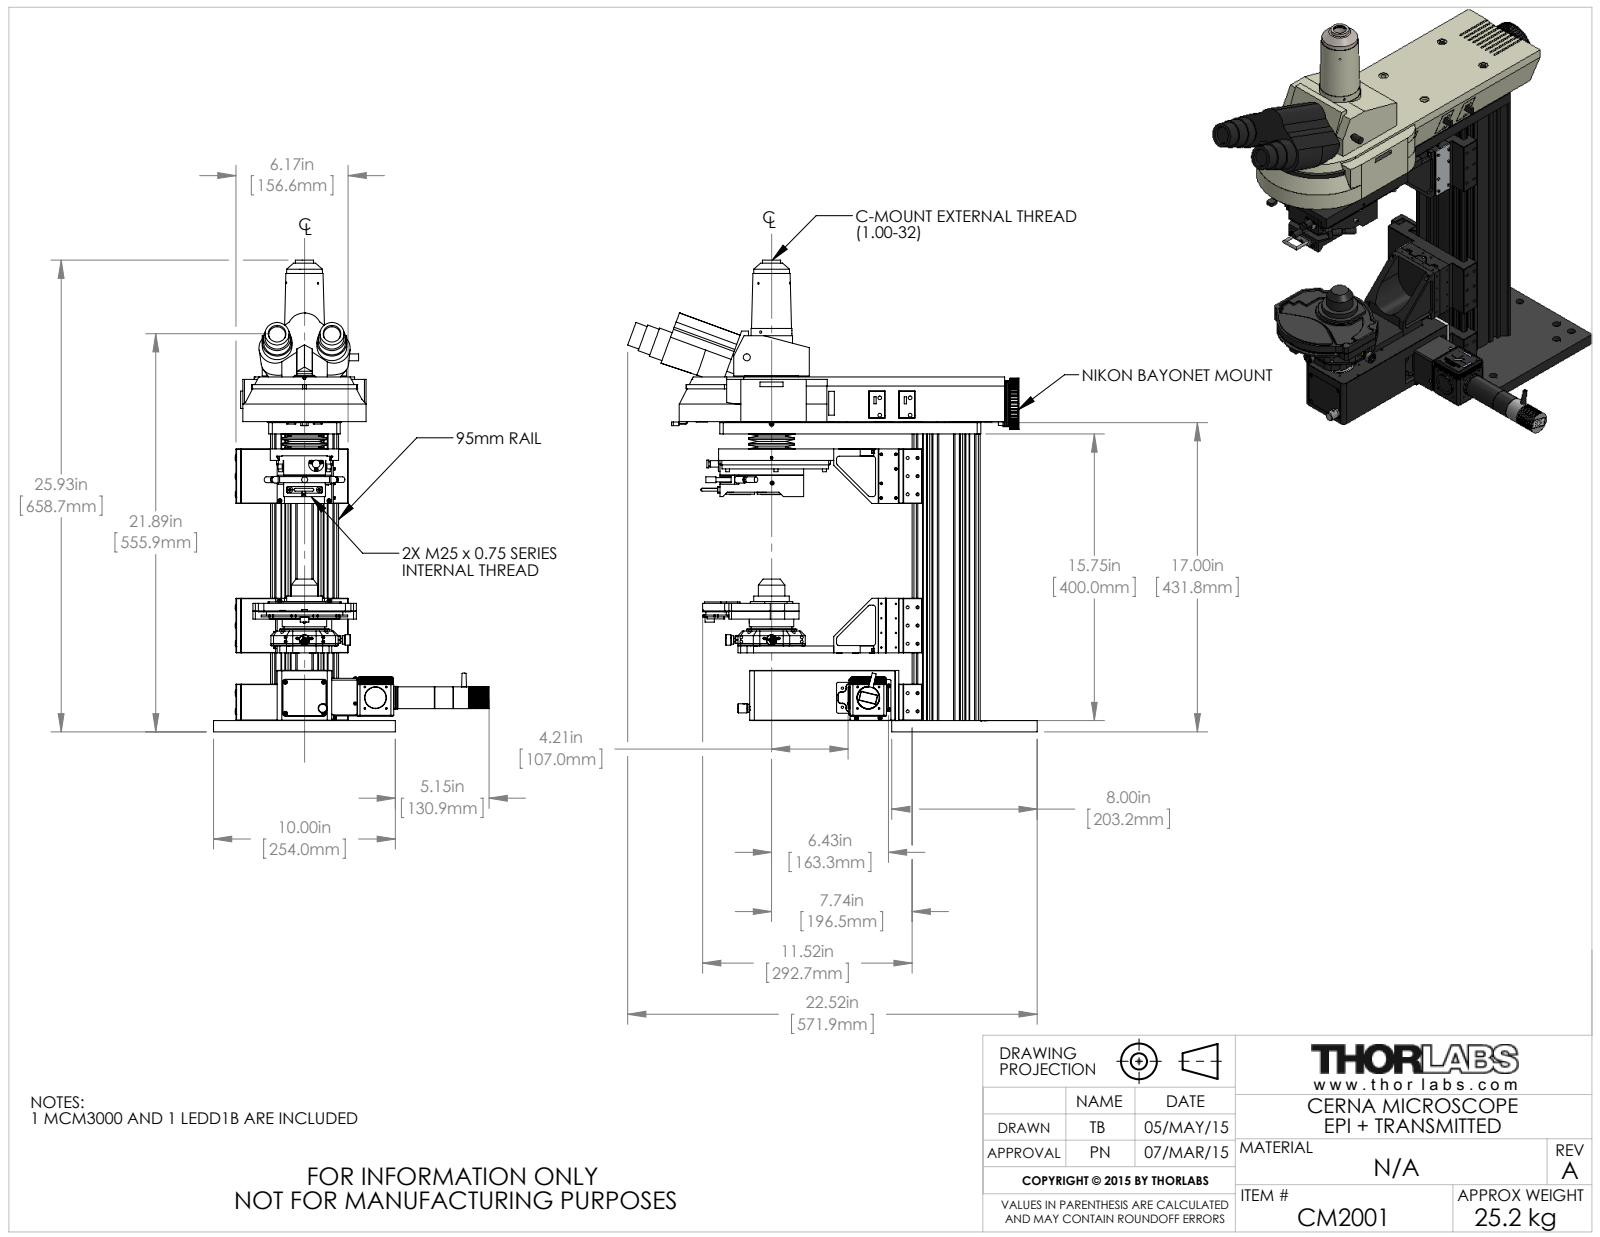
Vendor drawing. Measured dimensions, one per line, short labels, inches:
name: TTN041497-E0W
written by: SolidWorks 2014 (AUTOMOTIVE_DESIGN)
unit: in
bodies: 0 solids, 2158 faces (1211 planar, 743 cylindrical, 204 other)
size: 25.934 × 22.518 × 15.154
holes: 16× ⌀0.165, 14× ⌀0.266, 13× ⌀0.437, 8× ⌀0.22, 8× ⌀0.433, 6× ⌀0.07, 6× ⌀0.089, 5× ⌀0.13, 4× ⌀0.098, 4× ⌀0.13, 4× ⌀0.156, 4× ⌀0.2
bosses: 12× ⌀0.14, 5× ⌀0.215, 4× ⌀0.217, 3× ⌀0.183, 3× ⌀0.155, 2× ⌀1.64, 2× ⌀1.57, 2× ⌀1.5
rounds: 29× R0.05, 27× R0.025, 20× R0.1, 19× R0.15, 10× R0.5, 9× R0.06, 4× R0.08, 3× R0.108
face distances: 18.889, 0.625, 19.514, 17.054, 16.429, 2.46, 0.375, 10.839, 16.373, 15.748
hole spacings: 8.214, 1, 1.141, 0.55, 2.7, 0.8, 2, 8.232
